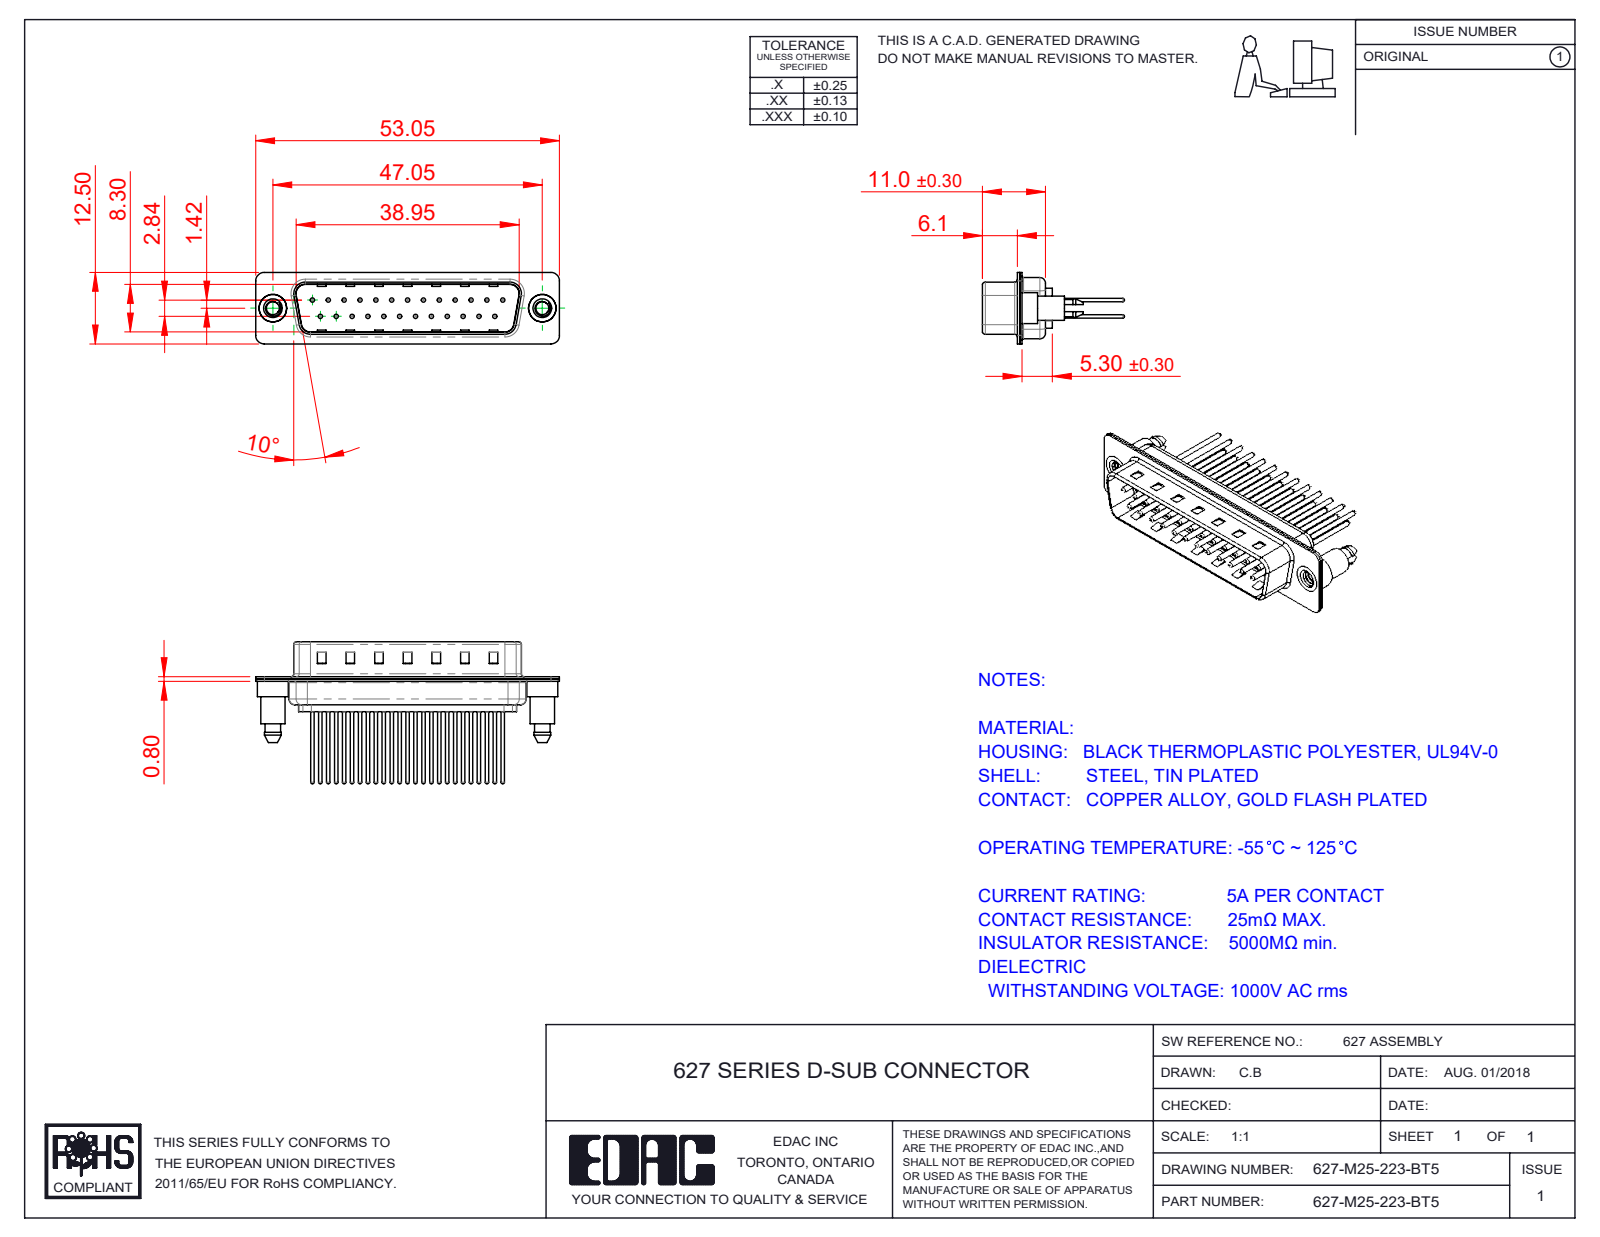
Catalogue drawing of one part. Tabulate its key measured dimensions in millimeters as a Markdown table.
| quantity | value |
| --- | --- |
| part name | 627M 4-40 Threaded Boardlock; 627-M25-223-BT5; 627M Shell Rear_25 Contacts; 627M Contact Row 2_23 (+3 more) |
| STEP written by | SolidWorks 2020 (CONFIG_CONTROL_DESIGN) |
| units | millimeters |
| bodies | 30 solids, 1351 faces (362 planar, 519 cylindrical, 470 other) |
| overall size | 53.05 × 24.77 × 12.5 |
| volume | 2 901 mm³ |
| surface area | 7 500 mm² |
| round holes (diameter × count) | 0.75 × 25, 1.6 × 25, 2 × 25, 2.26 × 2, 4 × 2, 4.8 × 2 |
| round bosses / shafts (diameter × count) | 1.5 × 25, 0.6 × 25, 5.4 × 2, 4.9 × 2, 4.25 × 2 |
| partial cylindrical surfaces (radius × count) | 1.5 × 18, 2 × 12, 1.6 × 10, 0.5 × 8, 0.25 × 4, 0.6 × 4, 0.65 × 4, 0.9 × 4 |
| main face-to-face distances | 0.4, 0.8, 9.5, 9.1, 8.7, 9.9, 1.2, 6.1, 5.7, 0.75 |
| hole center spacings | 3.16, 2.77, 5.54, 8.31, 11.08, 13.85, 16.62, 5.03 |
